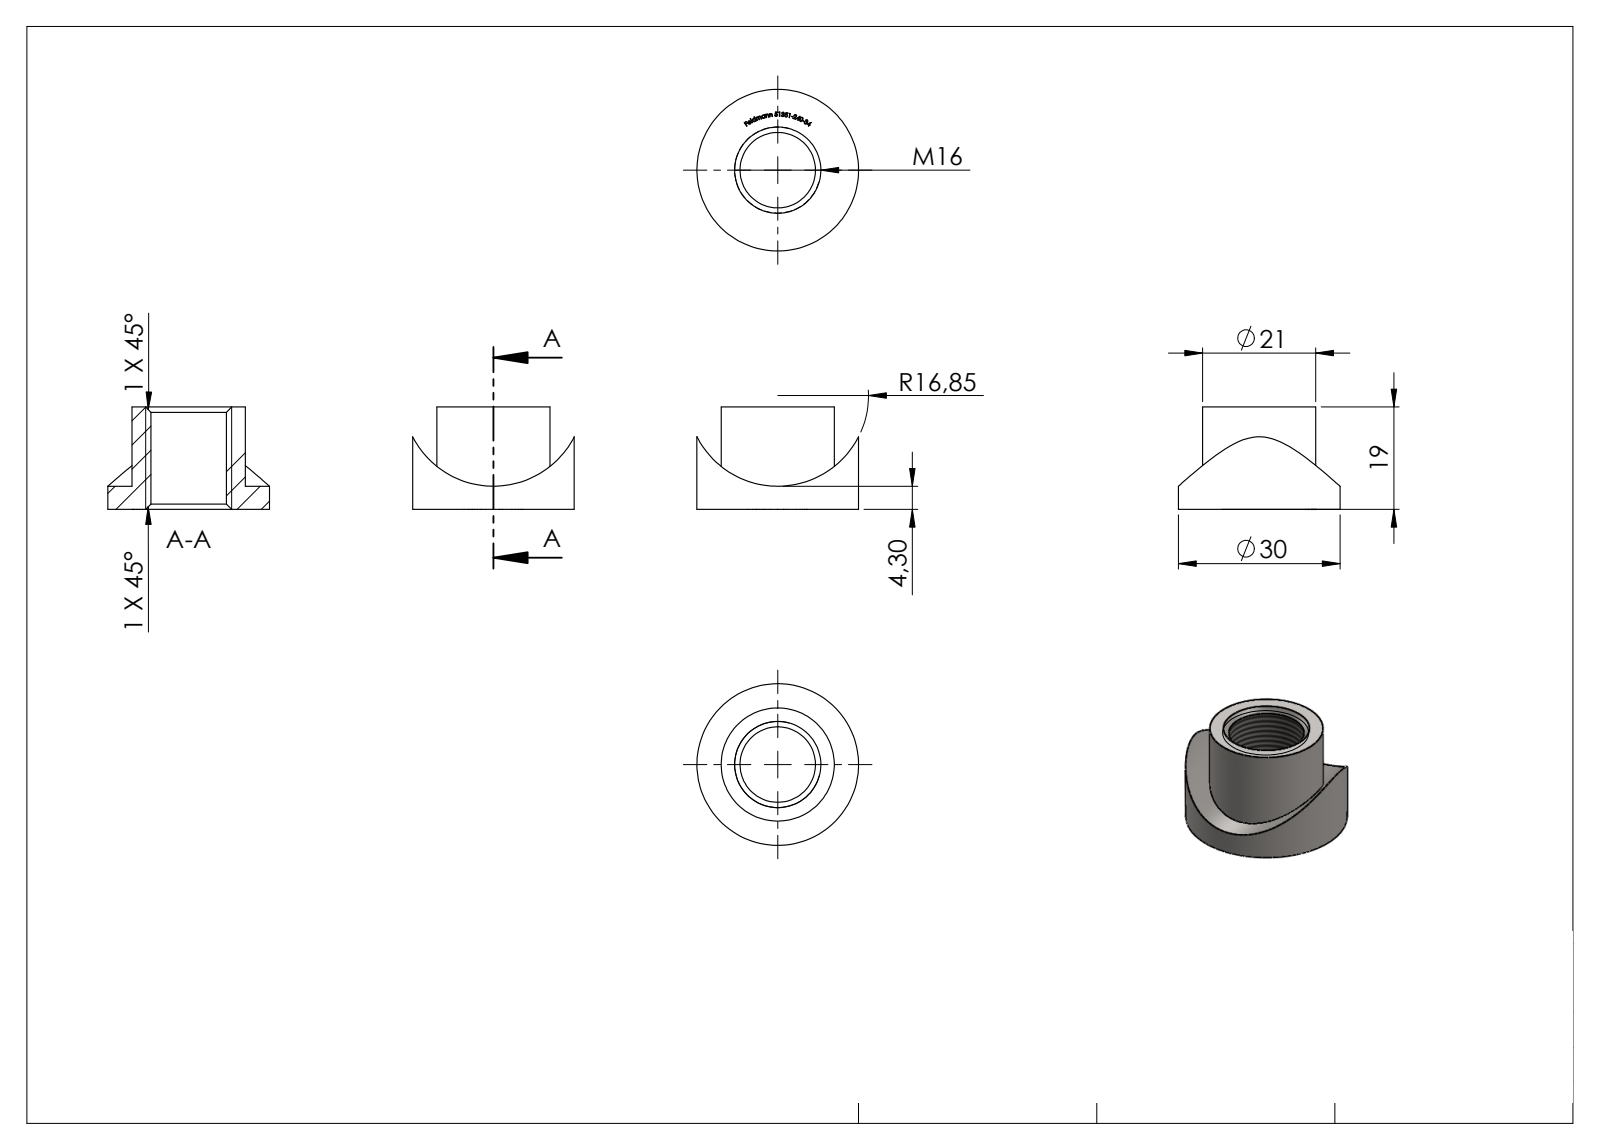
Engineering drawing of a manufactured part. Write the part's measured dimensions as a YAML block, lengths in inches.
part_name: "51351-240-34"
step_written_by: "SolidWorks 2015 (CONFIG_CONTROL_DESIGN)"
units: inches
bodies: {solids: 1, faces: 270, planar: 152, cylindrical: 7, other: 111}
overall_size: [1.181, 1.181, 0.748]
volume: 0.379
surface_area: 5.639
round_holes:
  - {diameter: 0.551, count: 1}
round_bosses_or_shafts:
  - {diameter: 1.181, count: 1}
  - {diameter: 0.827, count: 1}
partial_cylinders:
  - {radius: 0.663, count: 1}
face_to_face_distances: [0.748, 0.744, 0.016, 0.013, 0.017, 0.017, 0.015, 0.034, 0.031, 0.031]
